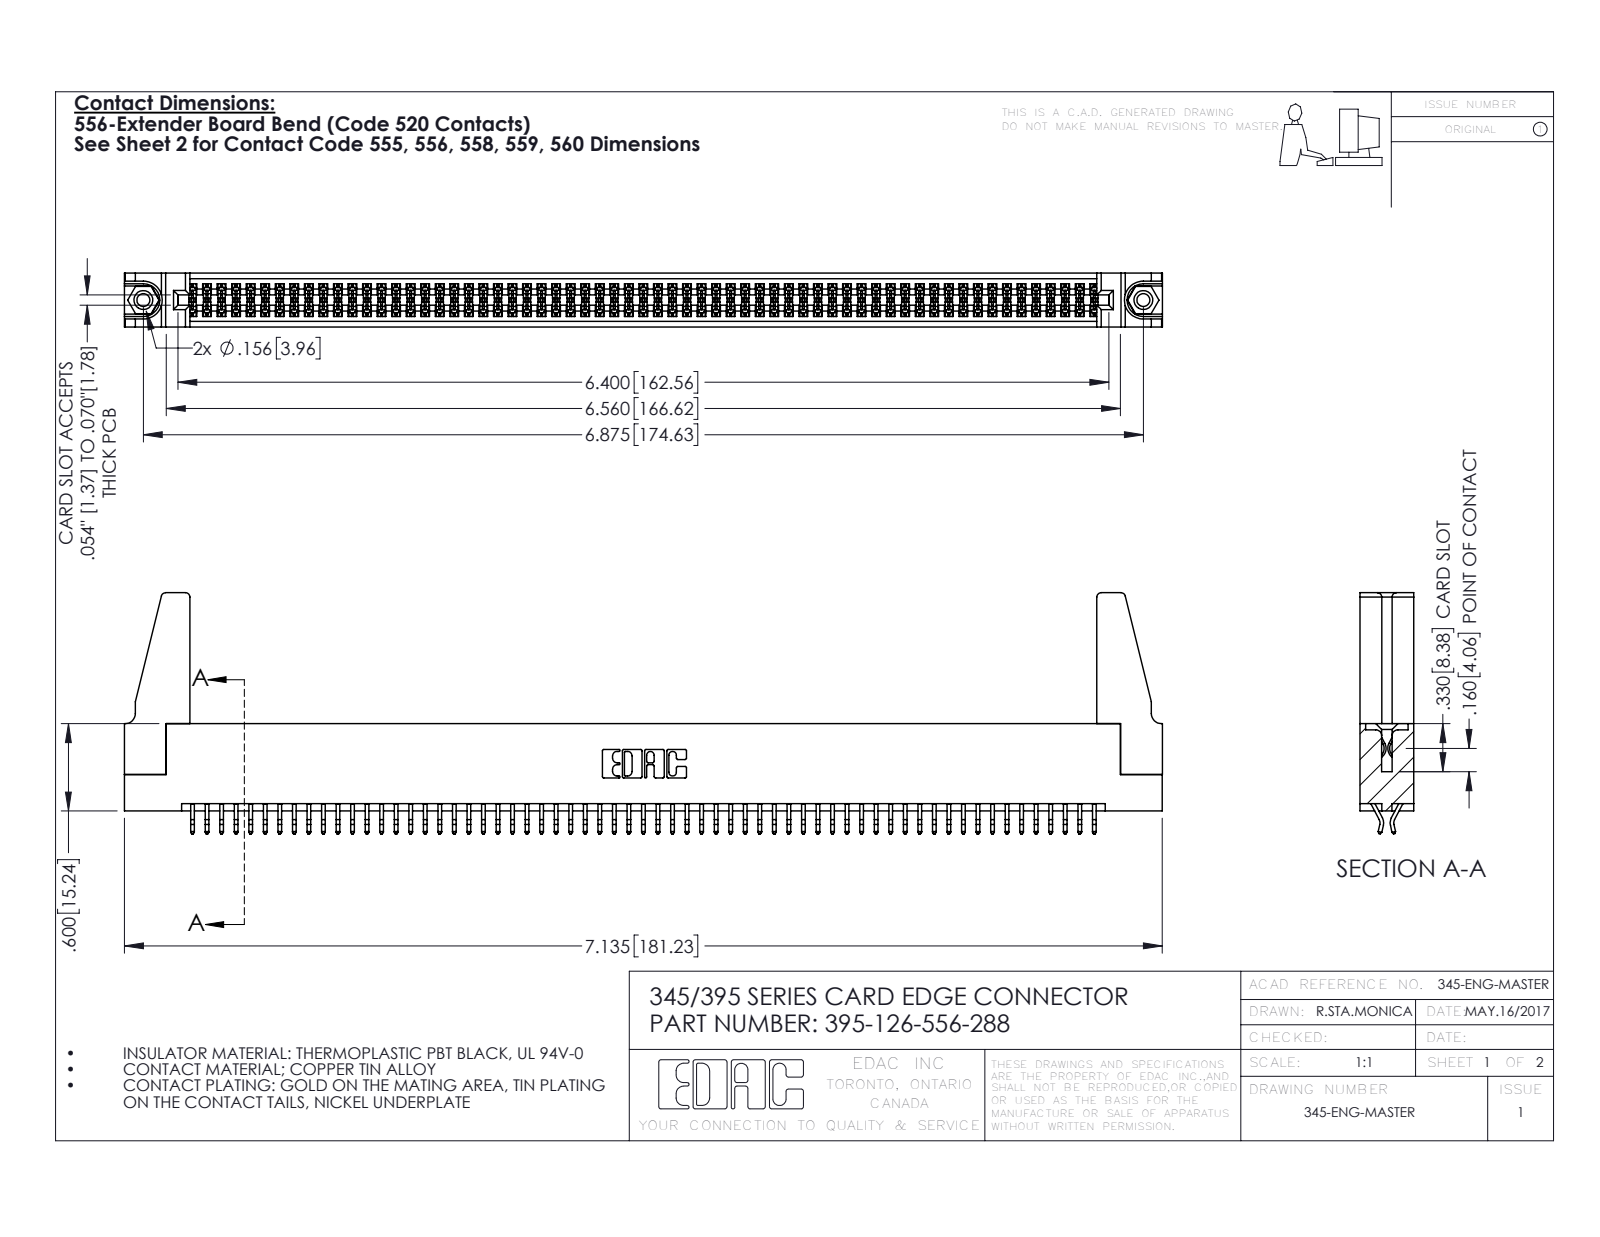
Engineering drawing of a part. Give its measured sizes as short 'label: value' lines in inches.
name: 345-292-001_556 Tail; 345-220-078_345-220-088; 395-126-556-288; 345-250-001_345-250-001-102 (+1 more)
written by: SolidWorks 2016 (CONFIG_CONTROL_DESIGN)
unit: in
bodies: 131 solids, 7306 faces (4814 planar, 2476 cylindrical, 16 other)
size: 7.136 × 1.657 × 0.37
volume: 1.285 in³; area: 46.08 in²
holes: 2× ⌀0.089, 2× ⌀0.125, 2× ⌀0.156, 1× ⌀0.064
bosses: 2× ⌀0.155
rounds: 189× R0.006, 22× R0.01, 8× R0.03, 6× R0.007, 6× R0.031, 3× R0.026, 2× R0.01, 2× R0.014
face distances: 0.072, 0.298, 0.37, 0.2, 0.025, 0.098, 0.272, 0.225, 0.175, 0.149
hole spacings: 0.27, 6.639, 6.875
